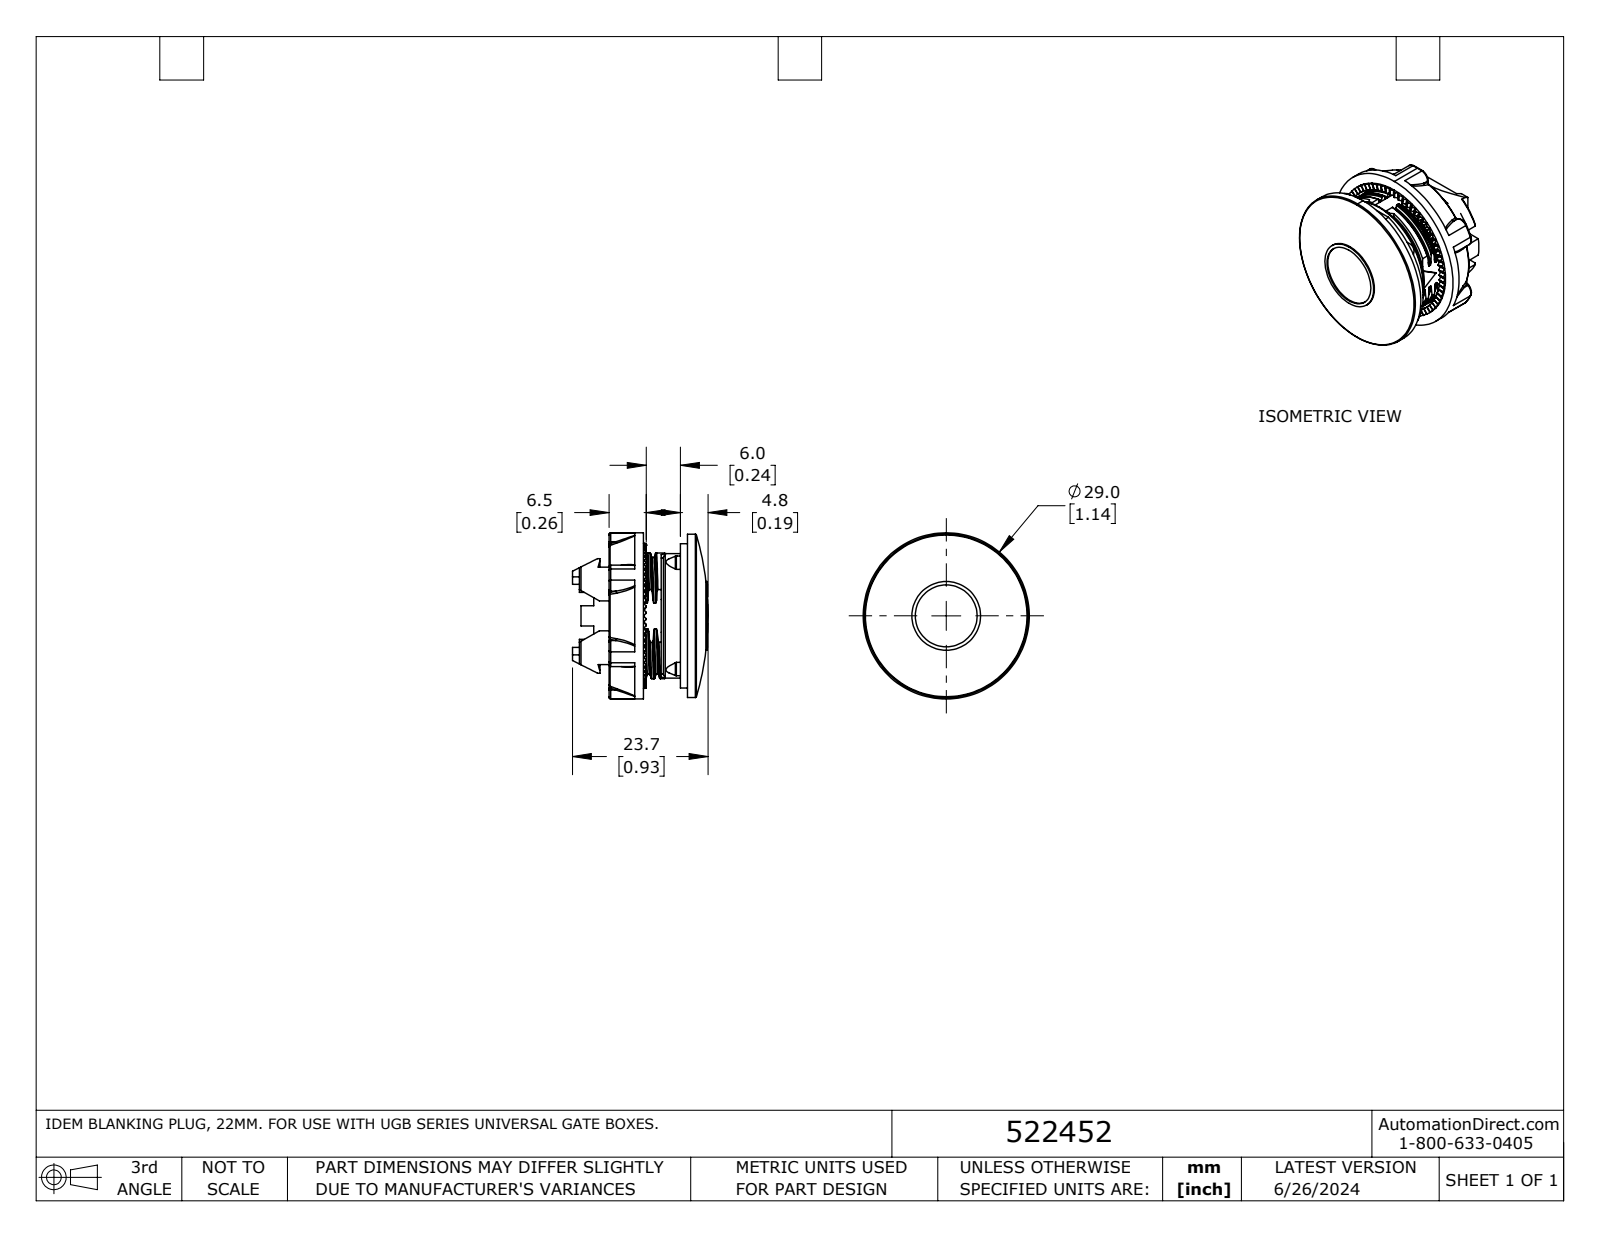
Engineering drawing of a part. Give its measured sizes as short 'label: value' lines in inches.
name: 522452
written by: SolidWorks 2023 (AUTOMOTIVE_DESIGN)
unit: in
bodies: 1 solid, 844 faces (402 planar, 212 cylindrical, 230 other)
size: 1.142 × 1.142 × 0.932
volume: 0.334 in³; area: 8.922 in²
holes: 1× ⌀0.425, 1× ⌀0.63, 1× ⌀0.882
bosses: 1× ⌀1.142, 1× ⌀1.122, 1× ⌀0.996, 1× ⌀0.856, 1× ⌀0.827, 1× ⌀0.787, 1× ⌀0.472
rounds: 36× R0.004, 18× R0.012, 12× R0.059, 4× R0.094, 3× R0.008, 3× R0.118, 2× R0.014, 2× R0.48
face distances: 0.236, 0.255, 0.491, 0.795, 0.049, 0.54, 0.304, 0.039, 0.265, 0.501
